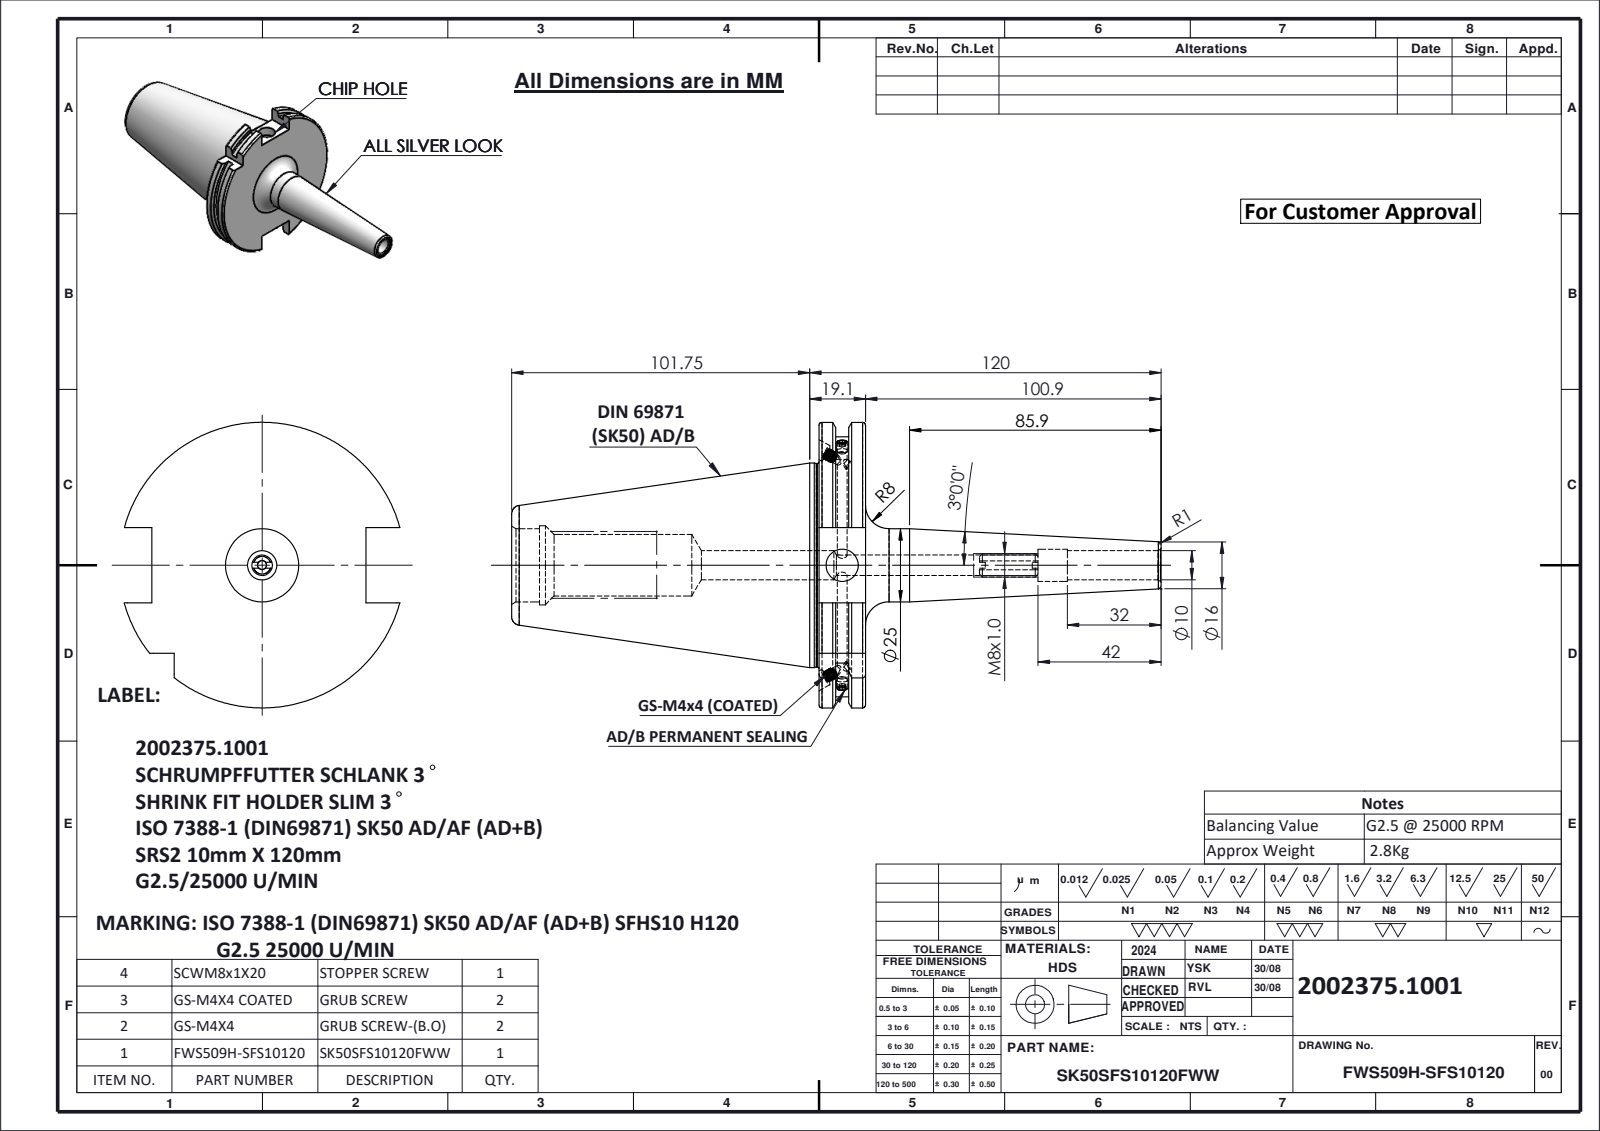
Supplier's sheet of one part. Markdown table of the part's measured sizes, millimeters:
| quantity | value |
| --- | --- |
| part name | GS-M4X4-COATING_DIN 913 - M4 x 4-N; SK50SFS10120FWW; GS-M4X4_DIN 913 - M4 x 4-N; SCWM8X1 (+1 more) |
| STEP written by | SolidWorks 2024 (CONFIG_CONTROL_DESIGN) |
| units | millimeters |
| bodies | 6 solids, 280 faces (79 planar, 81 cylindrical, 120 other) |
| overall size | 221.75 × 97.5 × 94.05 |
| volume | 366 351 mm³ |
| surface area | 53 241 mm² |
| round holes (diameter × count) | 3.2 × 2, 6 × 2, 11 × 2, 3 × 1, 3.3 × 1, 7 × 1, 10 × 1, 21 × 1, 25 × 1, 27 × 1 |
| round bosses / shafts (diameter × count) | 4 × 4, 2.9 × 2, 69.85 × 1, 69.45 × 1, 8 × 1 |
| partial cylindrical surfaces (radius × count) | 44.9 × 1, 48.75 × 1 |
| main face-to-face distances | 15.9, 5.66, 10.24, 10.14, 4.48, 5.76, 104.95, 110.61, 115.09, 120.85 |
